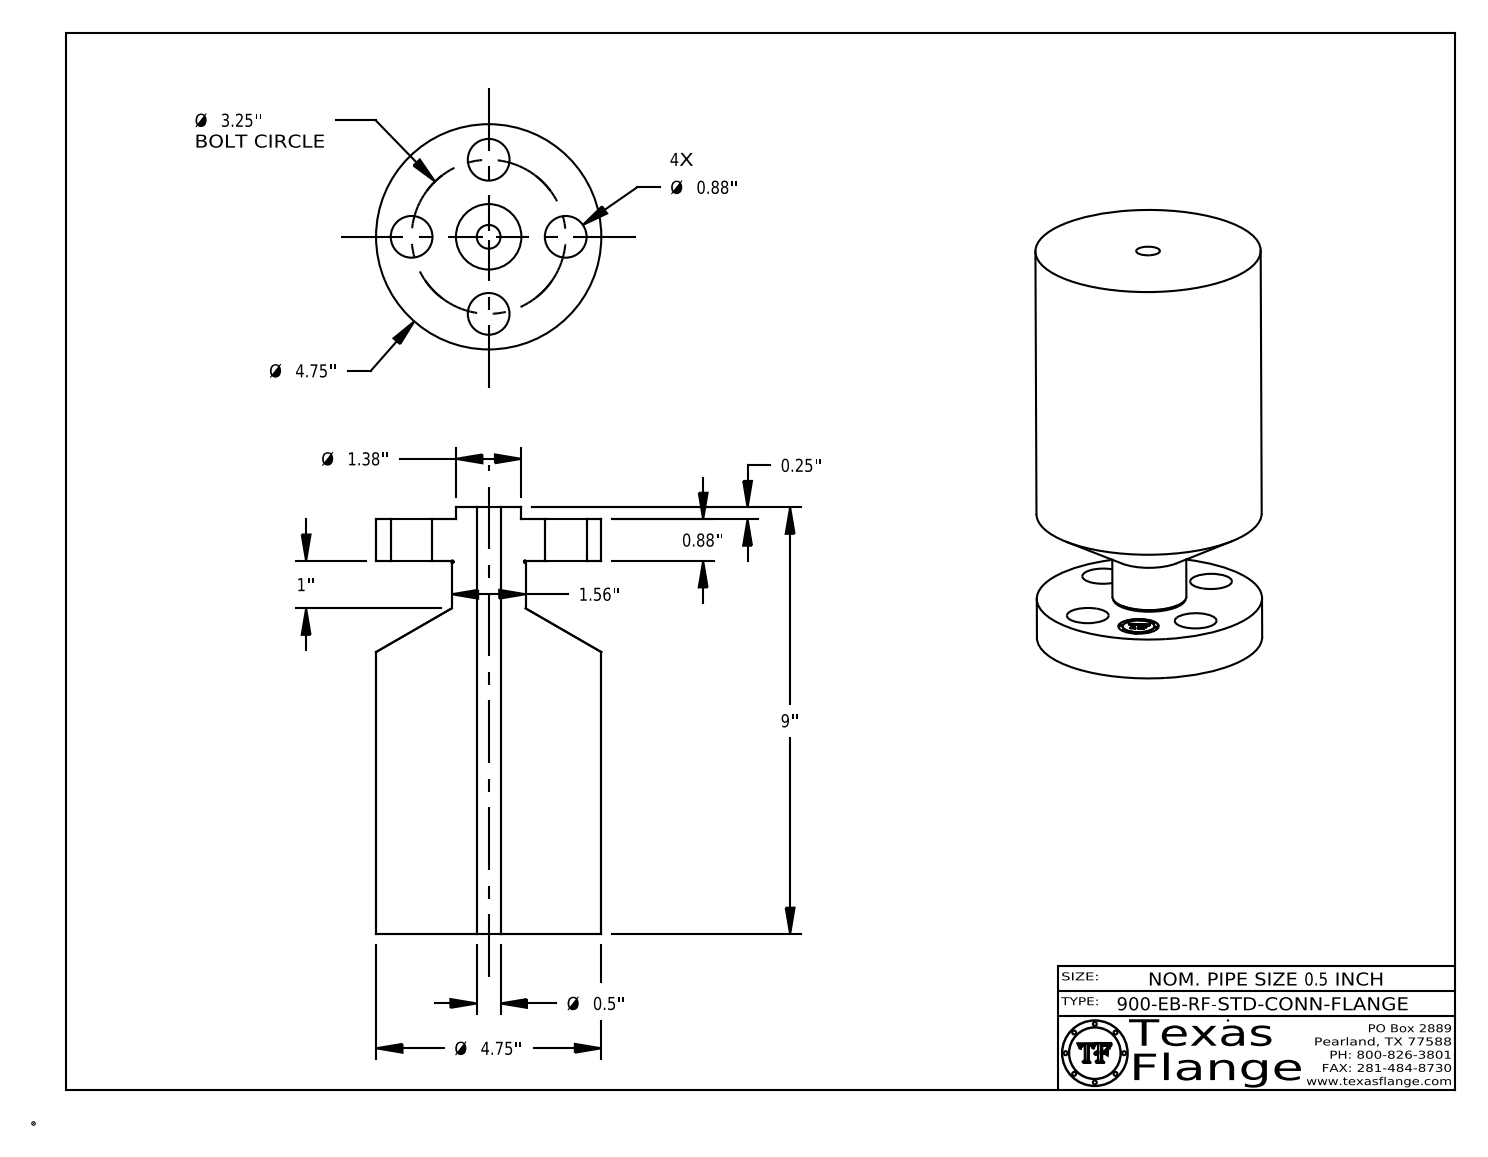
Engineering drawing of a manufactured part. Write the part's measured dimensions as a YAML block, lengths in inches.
part_name: "0.5-900-EB-RF-STD-CONN-FLANGE"
step_written_by: "CATIA V5 STEP AP214 (AUTOMOTIVE_DESIGN)"
units: inches
bodies: {solids: 1, faces: 413, planar: 369, cylindrical: 38, other: 6}
overall_size: [9, 4.75, 4.75]
volume: 127.2
surface_area: 196.2
round_holes:
  - {diameter: 0.88, count: 4}
  - {diameter: 0.5, count: 1}
  - {diameter: 0.85, count: 1}
round_bosses_or_shafts:
  - {diameter: 0.051, count: 8}
  - {diameter: 4.75, count: 1}
  - {diameter: 1.56, count: 1}
  - {diameter: 1.38, count: 1}
  - {diameter: 0.67, count: 1}
face_to_face_distances: [8.75, 0.88, 7.87, 0.25, 1.13, 9, 1.125, 0.875, 7.875, 0.254]
hole_center_spacings: [1.625, 2.298, 1.244, 3.003, 3.25]
